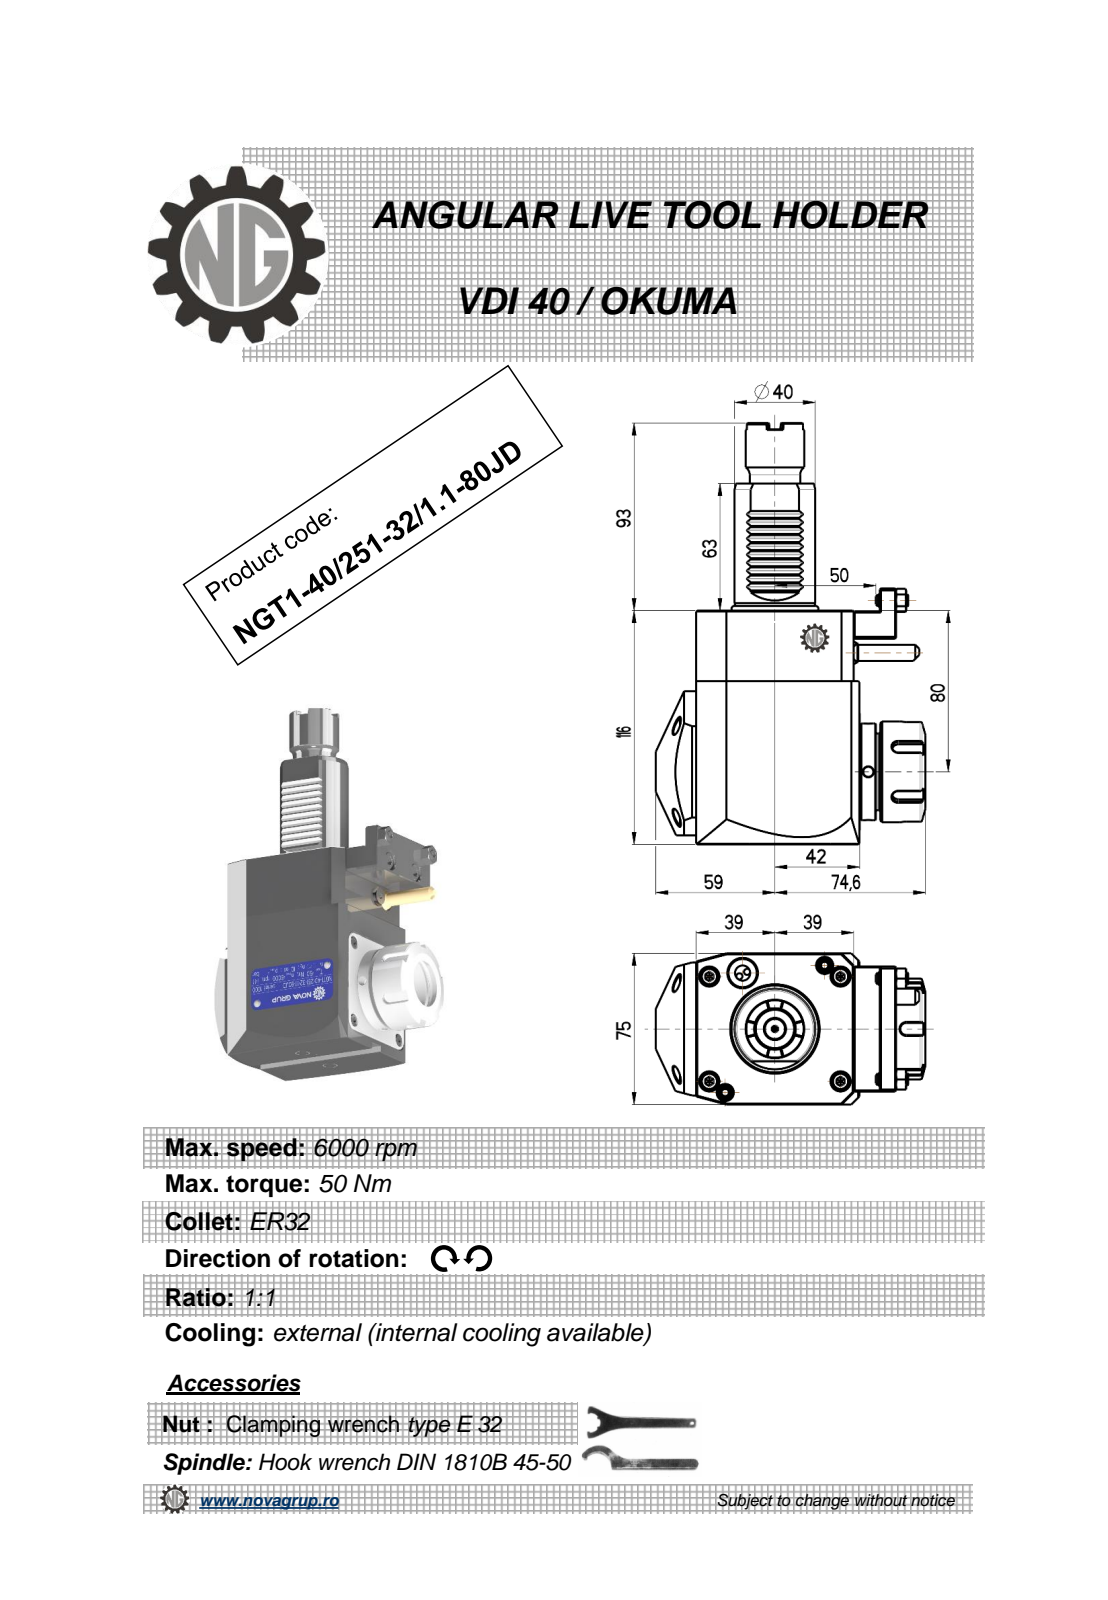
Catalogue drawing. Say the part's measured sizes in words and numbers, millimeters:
The part is named "NGT1_40_251_32_1_1_80JD". Its 3-D file was written by "PRO/ENGINEER BY PARAMETRIC TECHNOLOGY CORPORATION, 2010280 (CONFIG_CONTROL_DESIGN)". It is 1 solid with 456 faces: 195 planar, 86 cylindrical and 175 other. Overall it measures 209 by 133.6 by 76.6 millimeters. Its volume is 910 638 cubic millimeters and its surface area 74 671 square millimeters. Round holes: 3 of diameter 5, 1 of diameter 3, 1 of diameter 27. Round bosses or shafts: 2 of diameter 6, 1 of diameter 50, 1 of diameter 48, 1 of diameter 41, 1 of diameter 40, 1 of diameter 29, 1 of diameter 25, 1 of diameter 10. Partial cylindrical surfaces (rounded edges, fillets, slot ends): 10 of radius 0.3, 10 of radius 0.31, 6 of radius 0.2, 5 of radius 3, 1 of radius 0.5, 1 of radius 10, 1 of radius 40. The main face-to-face distances are 75, 116, 81, 0.5, 18, 21, 80.8, 10, 14, 3. The hole center spacings are 61.13.
